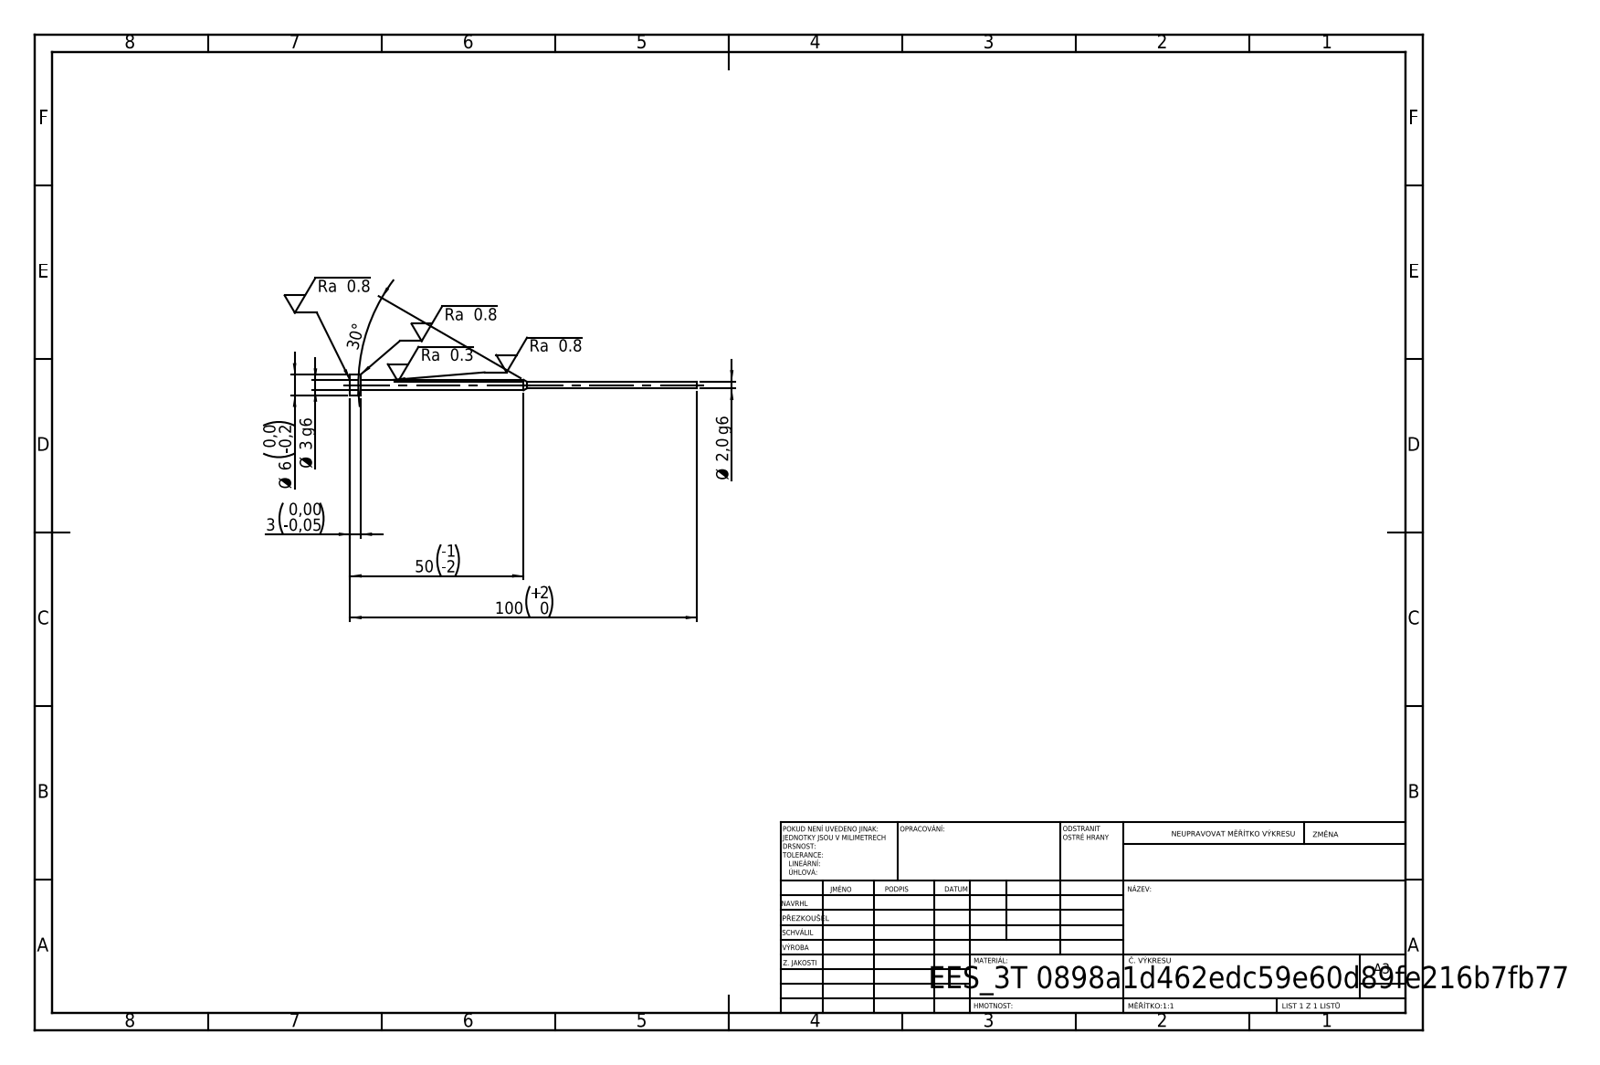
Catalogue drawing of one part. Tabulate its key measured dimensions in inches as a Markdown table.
| quantity | value |
| --- | --- |
| STEP written by | SolidWorks 2019 (CONFIG_CONTROL_DESIGN) |
| units | inches |
| bodies | 1 solid, 11 faces (3 planar, 6 cylindrical, 2 other) |
| overall size | 3.937 × 0.236 × 0.236 |
| volume | 0.035 in³ |
| surface area | 1.35 in² |
| round bosses / shafts (diameter × count) | 0.236 × 1, 0.118 × 1, 0.079 × 1 |
| main face-to-face distances | 0.118, 3.819, 3.937 |
